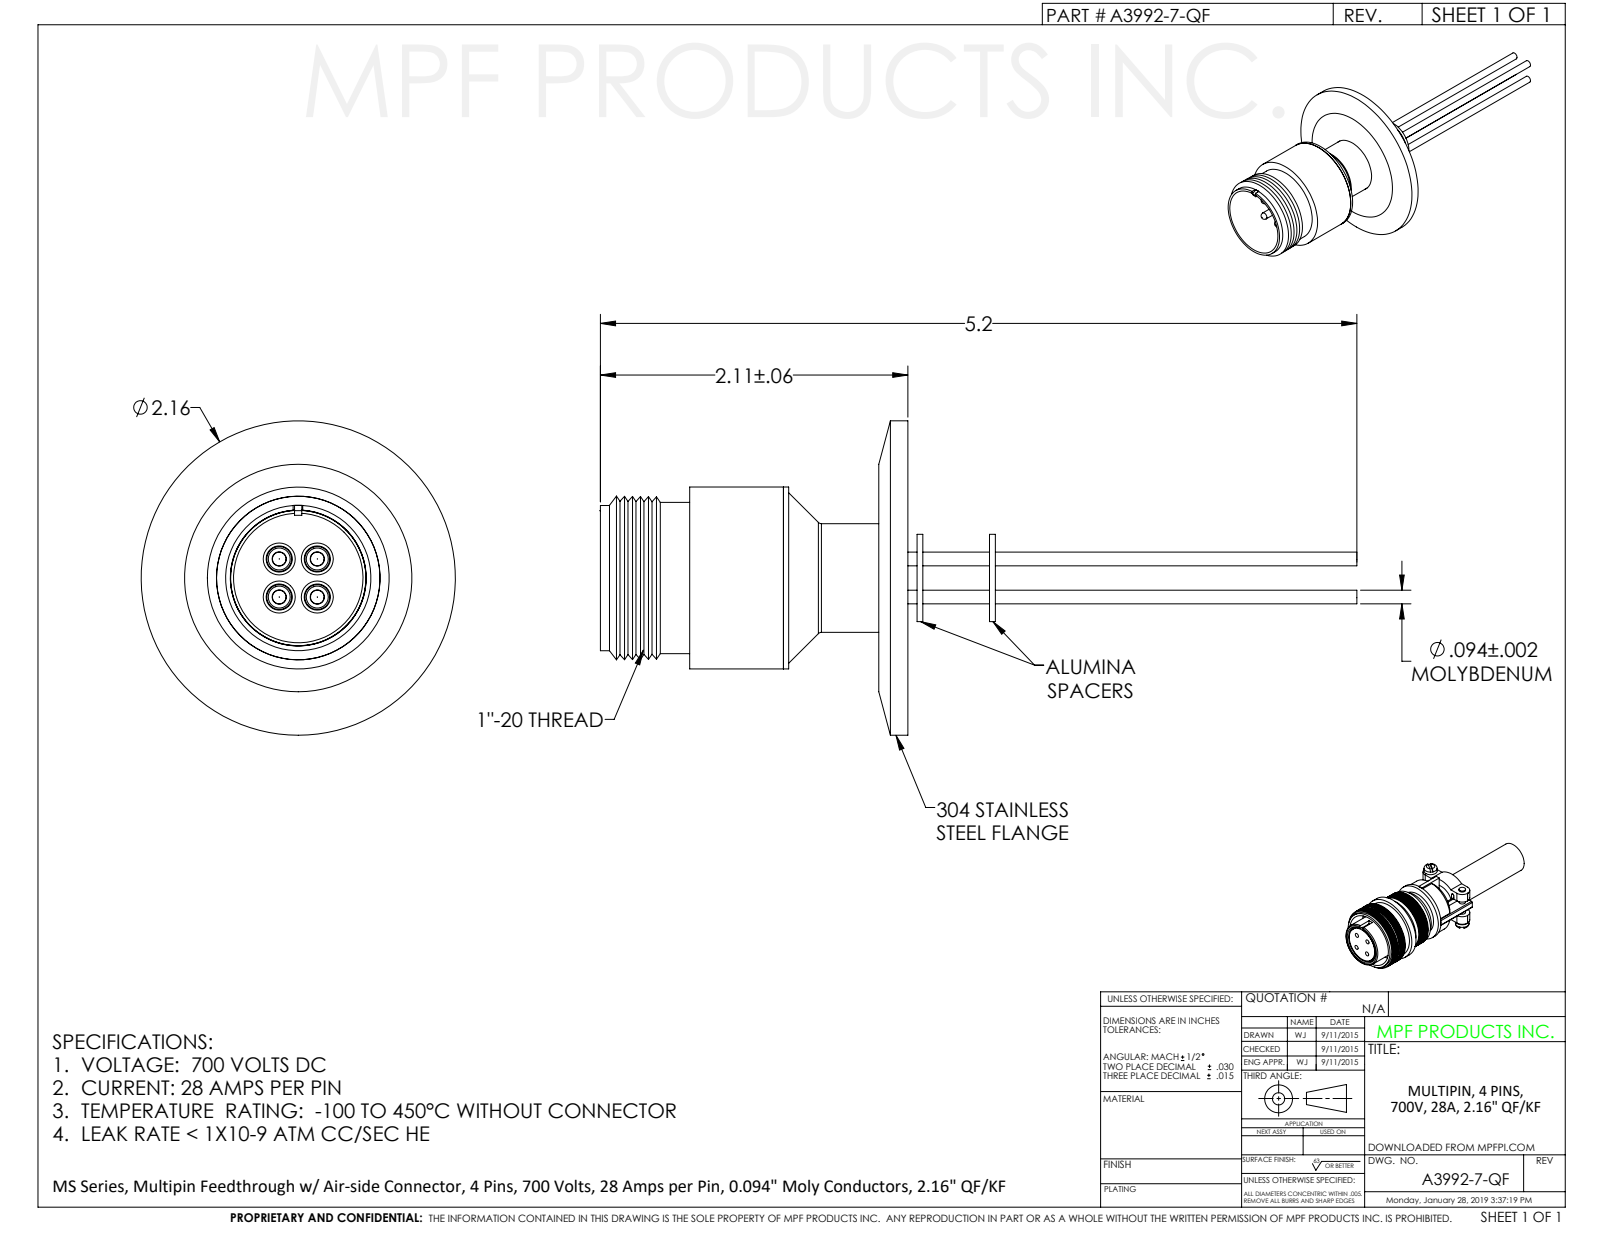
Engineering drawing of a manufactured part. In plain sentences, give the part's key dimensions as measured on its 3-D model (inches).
The part is named "A3992-7-QF". Its 3-D file was written by "SolidWorks 2017 (CONFIG_CONTROL_DESIGN)". It is 1 solid with 215 faces: 42 planar, 99 cylindrical and 74 other. Overall it measures 5.199 by 2.16 by 2.16 inches. Its volume is 1.197 cubic inches and its surface area 33.58 square inches. Round holes: 4 of diameter 0.151, 2 of diameter 0.098, 1 of diameter 0.675, 1 of diameter 0.932, 1 of diameter 0.935, 1 of diameter 0.98, 1 of diameter 1.16, 1 of diameter 1.63. Round bosses or shafts: 4 of diameter 0.182, 4 of diameter 0.171, 4 of diameter 0.094, 1 of diameter 2.16, 1 of diameter 1.25, 1 of diameter 1.06, 1 of diameter 1.04, 1 of diameter 0.999. The main face-to-face distances are 0.105, 0.2, 0.095, 1.193, 1.088, 0.993, 0.04, 0.843, 1.5, 1.395. The hole center spacings are 0.131, 0.185, 0.261, 0.296, 0.135, 0.37, 0.27.
